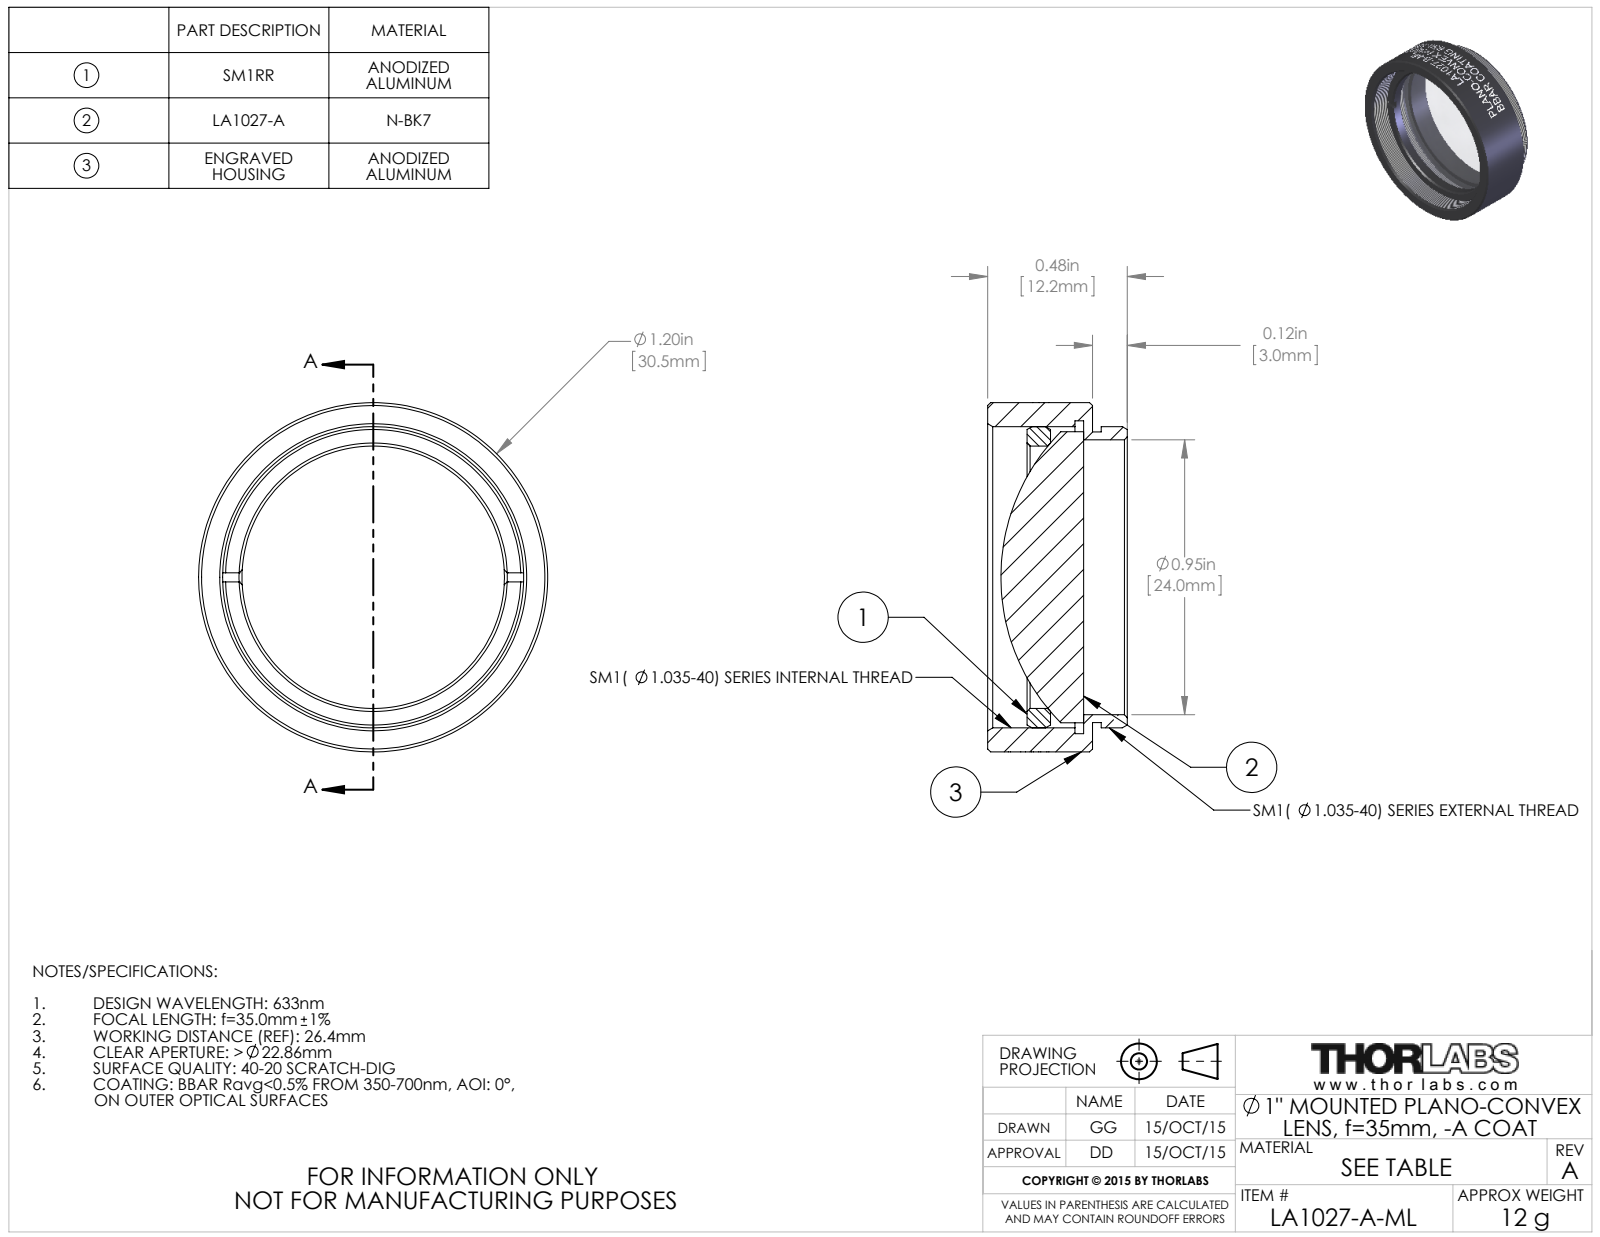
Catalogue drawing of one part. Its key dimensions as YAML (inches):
part_name: "TTN039474-E0W"
step_written_by: "SolidWorks 2014 (CONFIG_CONTROL_DESIGN)"
units: inches
bodies: {solids: 3, faces: 147, planar: 20, cylindrical: 103, other: 24}
overall_size: [1.2, 1.2, 0.48]
volume: 0.283
surface_area: 7.028
round_holes:
  - {diameter: 0.902, count: 1}
  - {diameter: 0.945, count: 1}
  - {diameter: 1.075, count: 1}
round_bosses_or_shafts:
  - {diameter: 1.2, count: 1}
  - {diameter: 1.035, count: 1}
  - {diameter: 1, count: 1}
  - {diameter: 0.999, count: 1}
face_to_face_distances: [0.03, 0.36, 0.33, 0.144, 0.115, 0.215, 0.224, 0.194, 0.08, 0.135]
